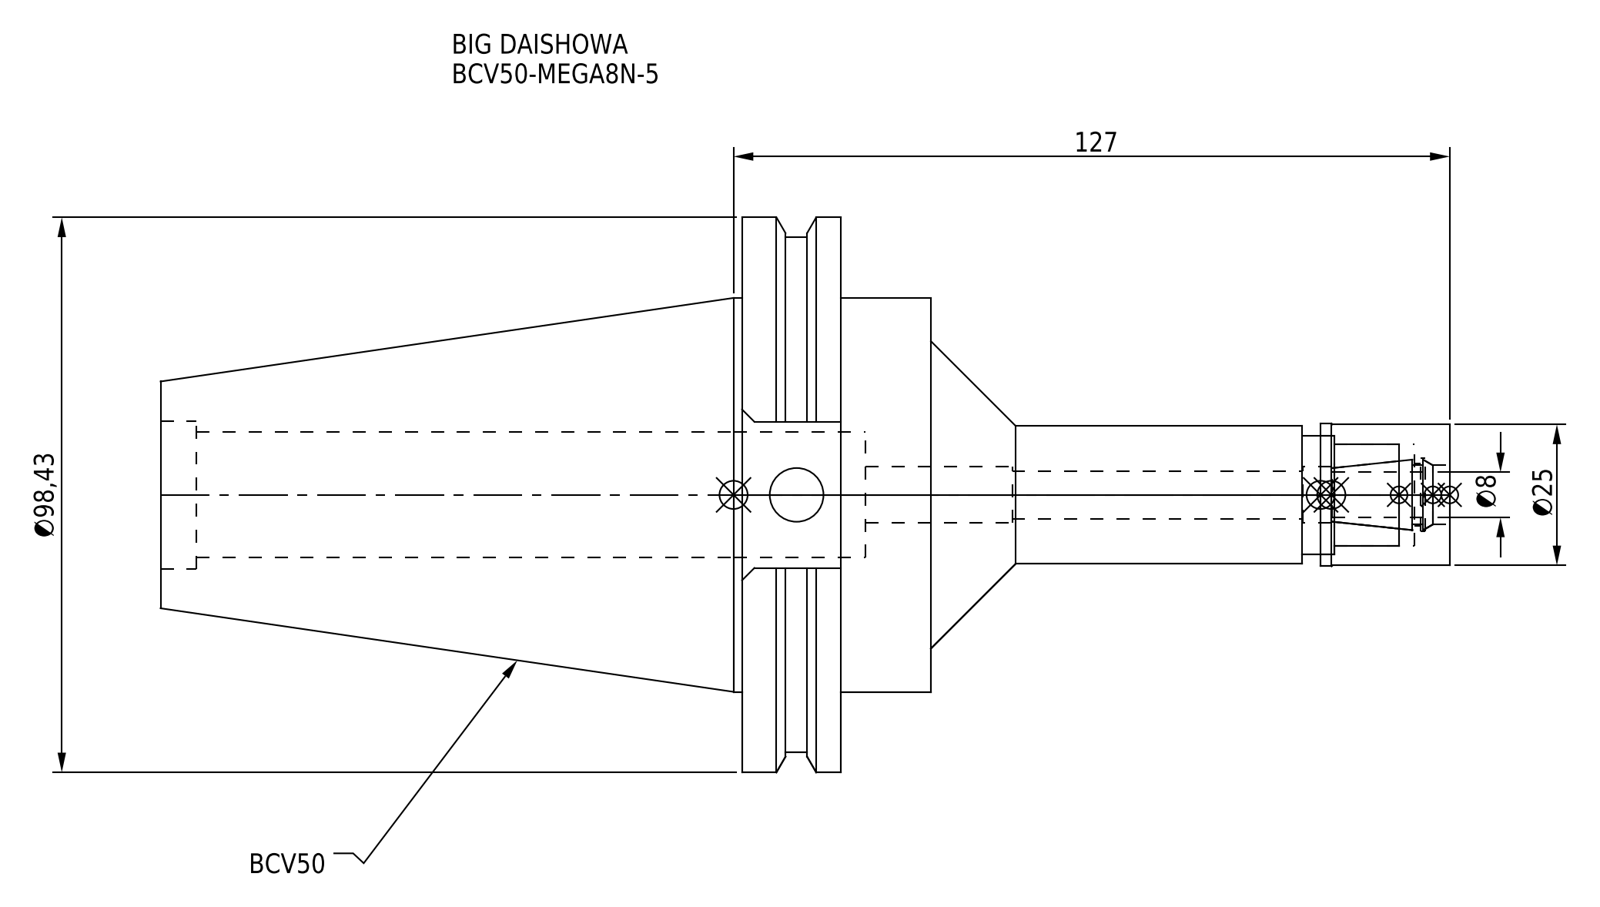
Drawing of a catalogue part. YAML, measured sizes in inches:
part_name: "MGN8_1.stp; DXF_TEMP_ASSY_ASM_4_ASM.stp; BCV50-MEGA8N-5_1.stp; BCV50MN08050-080_ASM.stp (+3 more)"
step_written_by: "SolidWorks 2019 (CONFIG_CONTROL_DESIGN)"
units: inches
bodies: {solids: 2, faces: 91, planar: 33, cylindrical: 44, other: 14}
overall_size: [9, 3.875, 3.738]
volume: 26.26
surface_area: 94.72
round_holes:
  - {diameter: 0.331, count: 1}
  - {diameter: 0.375, count: 1}
  - {diameter: 0.394, count: 1}
  - {diameter: 0.413, count: 1}
  - {diameter: 0.433, count: 1}
  - {diameter: 0.512, count: 1}
  - {diameter: 0.709, count: 1}
  - {diameter: 0.827, count: 1}
  - {diameter: 0.878, count: 1}
  - {diameter: 1.033, count: 1}
round_bosses_or_shafts:
  - {diameter: 3.875, count: 1}
  - {diameter: 3.594, count: 1}
  - {diameter: 2.75, count: 1}
  - {diameter: 0.996, count: 1}
  - {diameter: 0.984, count: 1}
  - {diameter: 0.965, count: 1}
face_to_face_distances: [0.691, 0.628, 1.319, 5.378, 4.75, 4.059, 3.622, 4.25, 4.941, 9]
